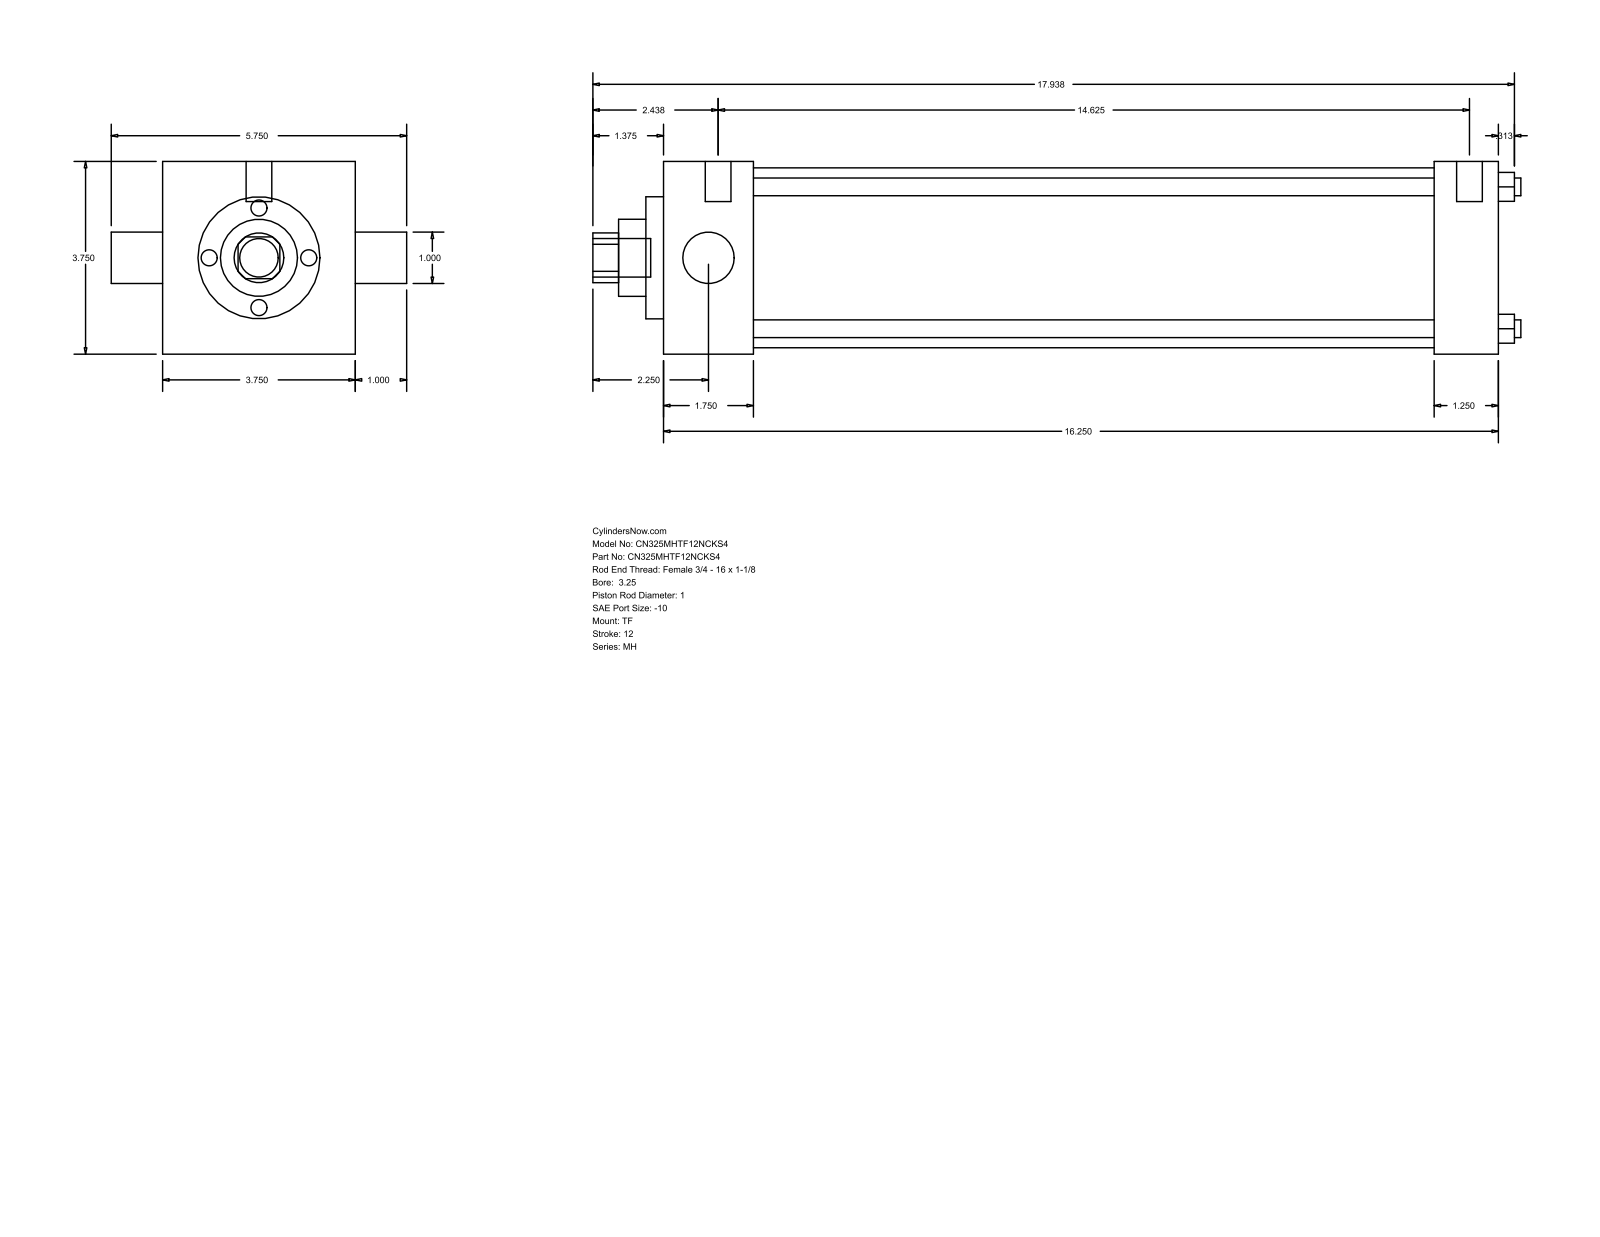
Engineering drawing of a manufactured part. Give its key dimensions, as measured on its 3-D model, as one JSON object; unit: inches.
{"part_name": "MH_TF__0325_1", "step_written_by": "GSSL Pune (CONFIG_CONTROL_DESIGN)", "units": "inches", "bodies": {"solids": 0, "faces": 86, "planar": 61, "cylindrical": 25, "other": 0}, "overall_size": [18.063, 5.75, 3.75], "round_holes": [[0.345, 4], [1, 2], [1.5, 1], [2.375, 1], [3.5, 1]], "round_bosses_or_shafts": [[0.219, 3], [0.5, 2], [0.75, 1]], "partial_cylinders_radius": [[0.484, 1]], "face_to_face_distances": [3.75, 16.25, 1.75, 15, 13.25, 14.5, 1.25, 0.344, 2.094, 15.344], "hole_center_spacings": [1.952, 2.76, 3.903]}
